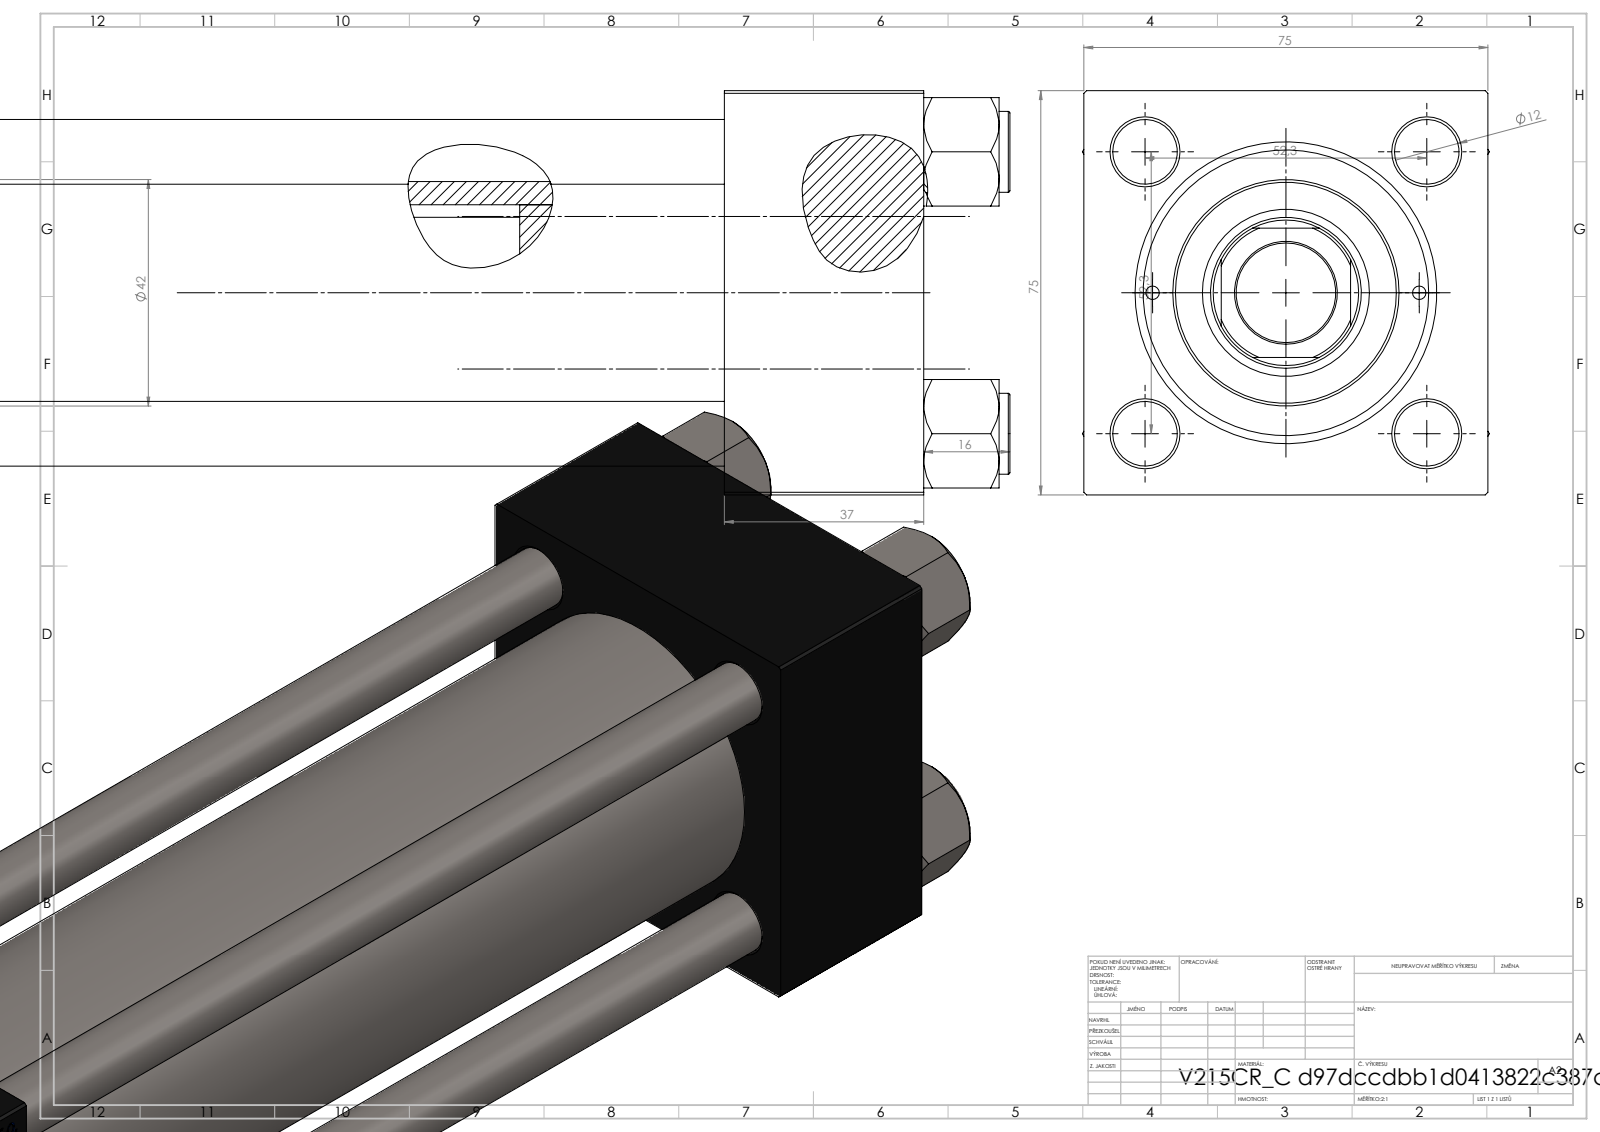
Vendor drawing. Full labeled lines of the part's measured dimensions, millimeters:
Part name (STEP PRODUCT): NUT_M5_C; V215_VC_A; V215CR_C_TYCINKA; V215CR_C_Body (+1 more)
STEP written by: SolidWorks 2019 (CONFIG_CONTROL_DESIGN)
Units: millimetres
Bodies: 11 solids, 1155 faces (528 planar, 91 cylindrical, 536 other)
Overall size (bounding box): 335 × 75.54 × 75
Volume: 888 417 mm³ · Surface area: 231 059 mm²
Round holes (diameter × count): ⌀12 ×4, ⌀2.5 ×2, ⌀7 ×2, ⌀20.96 ×2, ⌀30 ×2, ⌀18.5 ×1, ⌀28 ×1, ⌀31 ×1, ⌀41 ×1, ⌀50 ×1, ⌀53 ×1
Round bosses / shafts (diameter × count): ⌀15 ×4, ⌀56 ×1, ⌀42 ×1
Partial cylindrical surfaces — rounded edges, fillets, slot ends (radius × count): R13.5 ×1
Main face-to-face distances: 75, 37, 294, 257, 235, 198, 59, 265.3, 228.3, 30.3
Hole centre spacings: 26.19, 36.98, 52.3, 57.22, 24.75, 73.96, 49.5, 233.5
